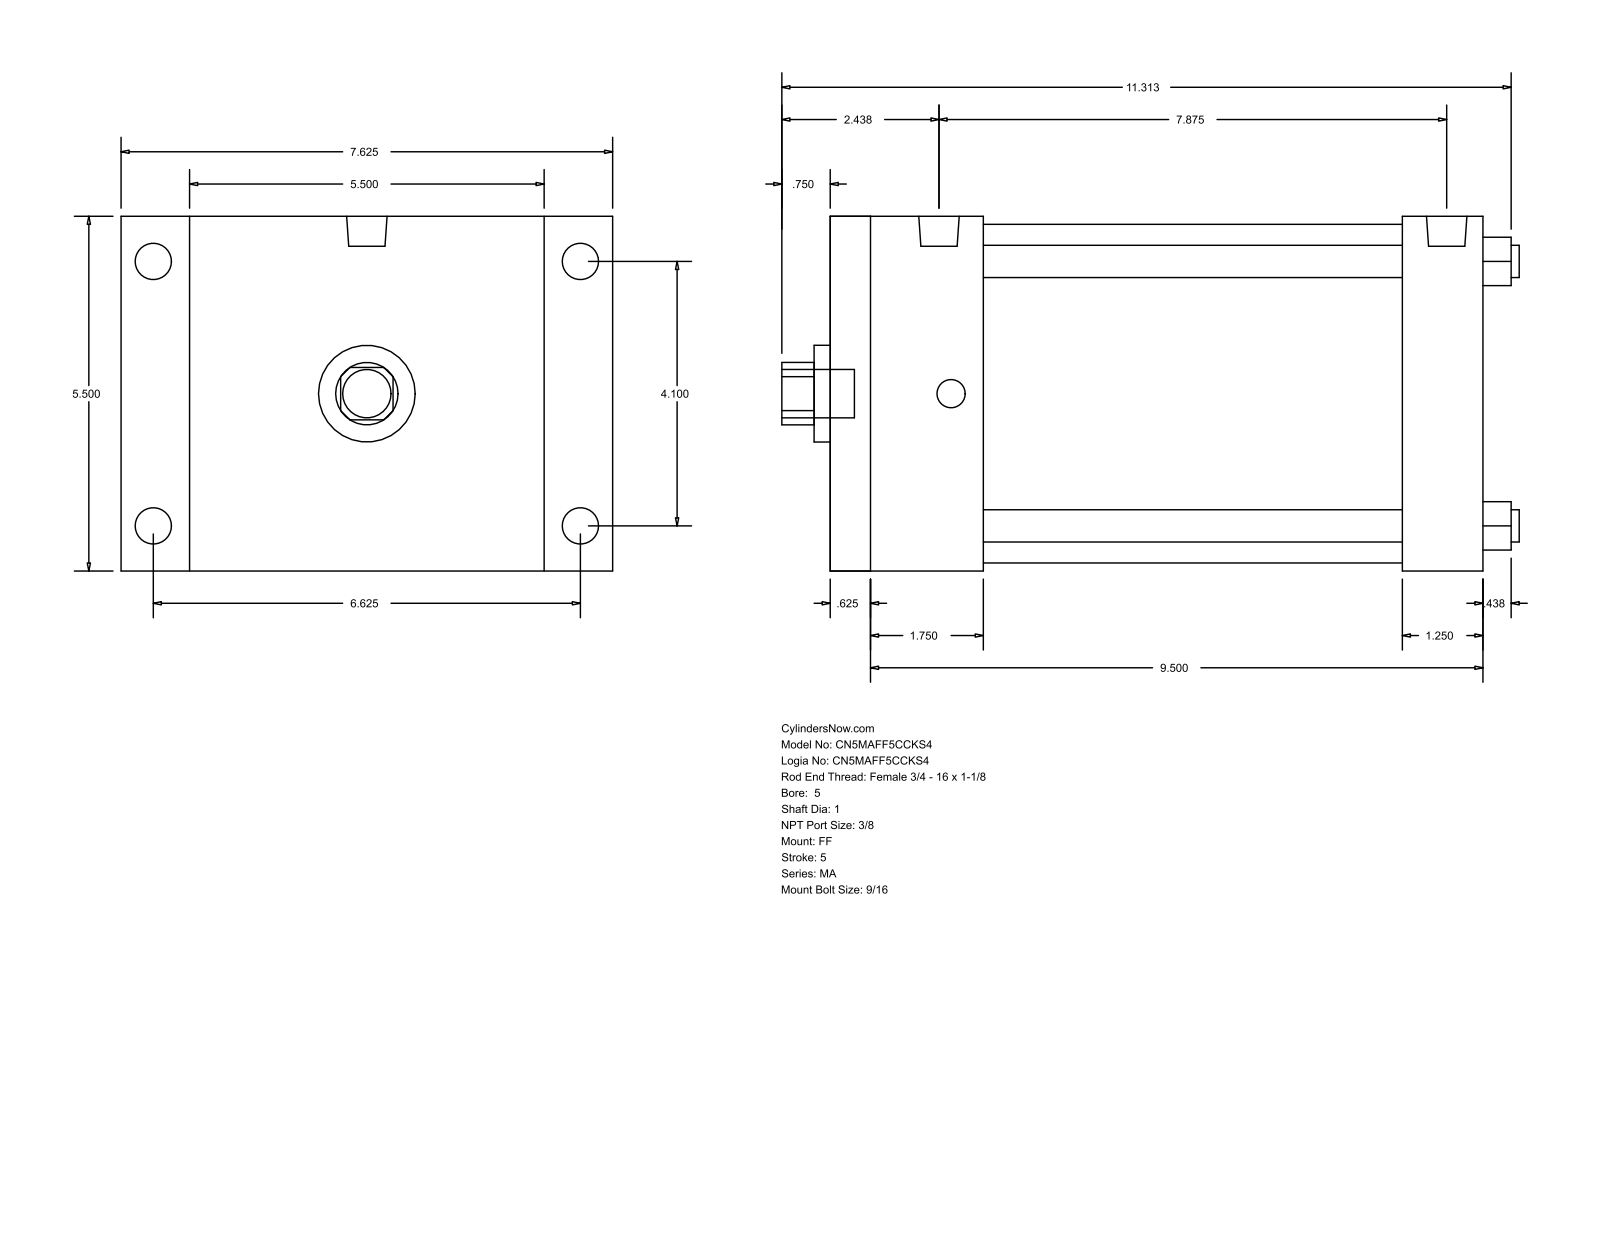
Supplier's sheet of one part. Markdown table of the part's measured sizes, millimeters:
| quantity | value |
| --- | --- |
| part name | MA_FF__0500_1 |
| STEP written by | GSSL Pune (CONFIG_CONTROL_DESIGN) |
| units | millimeters |
| bodies | 0 solids, 92 faces (64 planar, 28 cylindrical, 0 other) |
| overall size | 290.51 × 193.68 × 139.7 |
| round holes (diameter × count) | 12.7 × 4, 25.4 × 1, 38.1 × 1, 133.35 × 1 |
| round bosses / shafts (diameter × count) | 14.29 × 4, 11.11 × 4, 15.93 × 2, 19.05 × 1 |
| partial cylindrical surfaces (radius × count) | 12.29 × 1 |
| main face-to-face distances | 139.7, 257.18, 15.87, 241.31, 165.09, 225.42, 209.55, 31.76, 60.33, 44.46 |
| hole center spacings | 73.64, 104.14, 147.28 |
